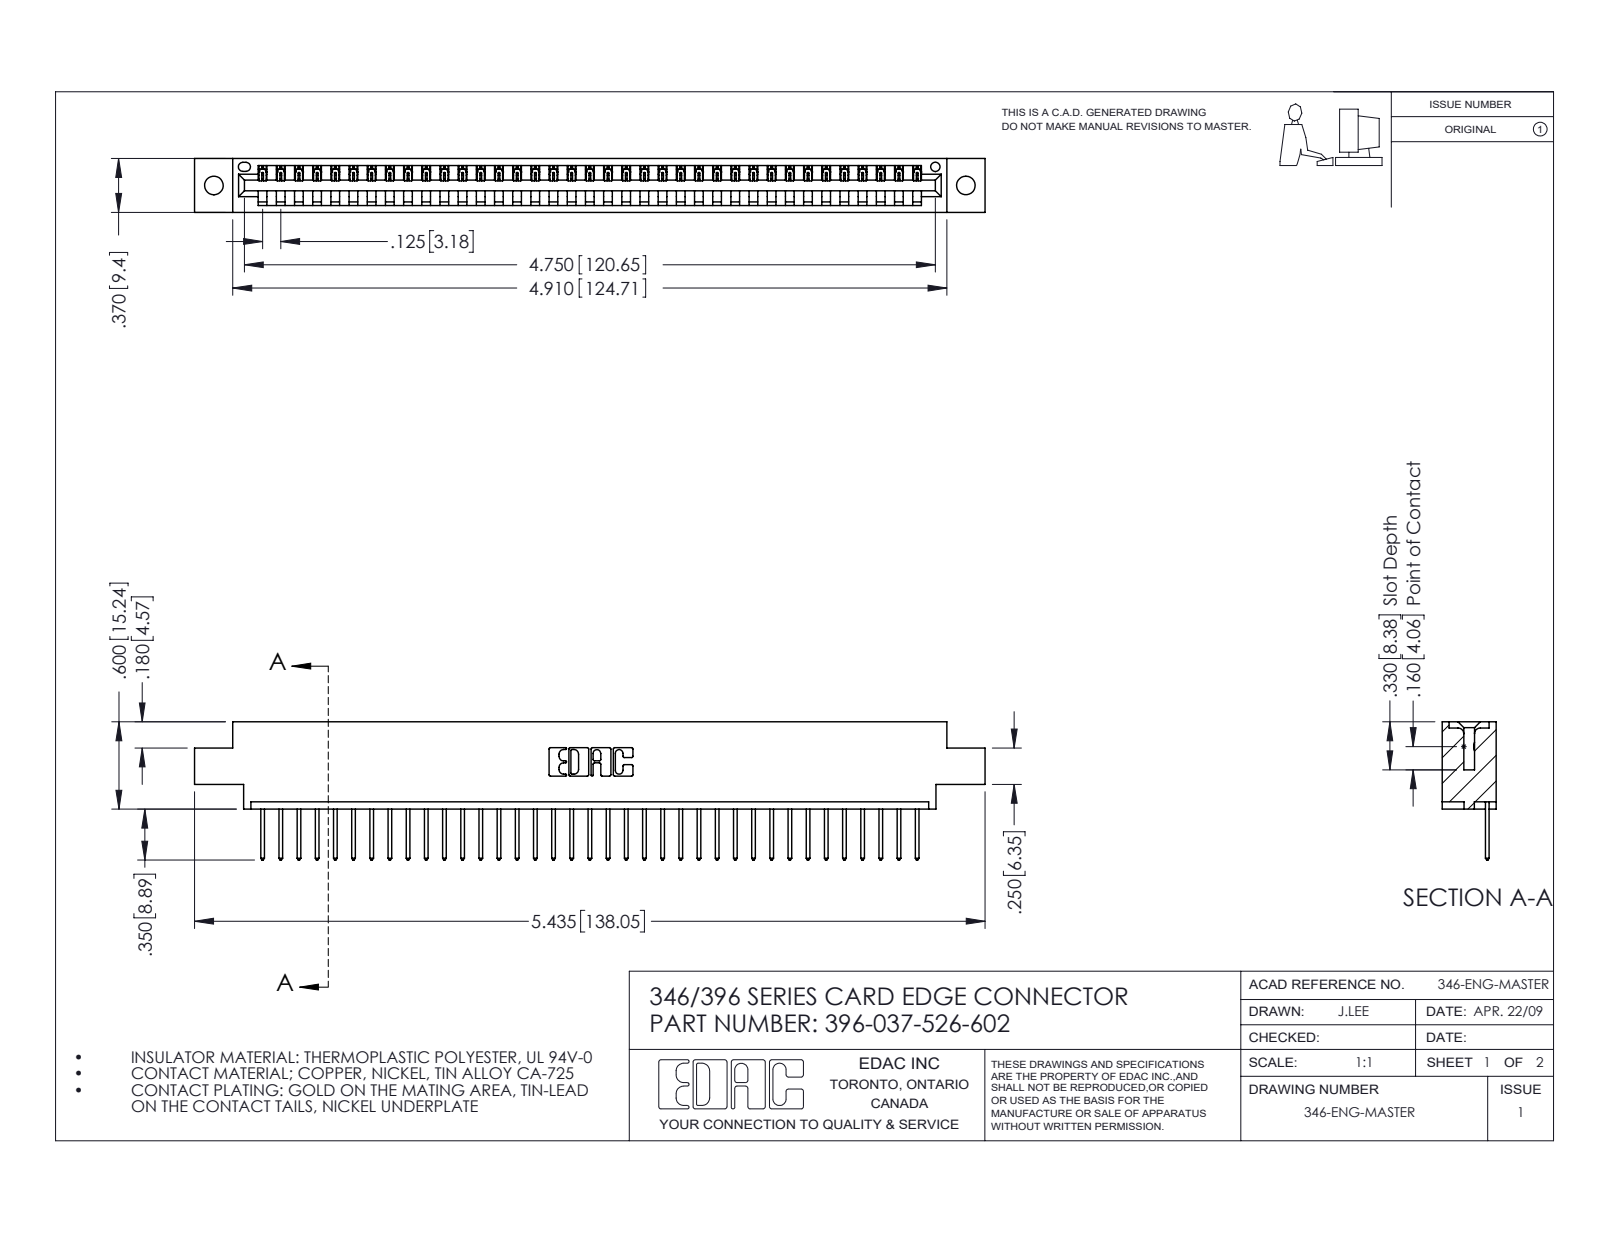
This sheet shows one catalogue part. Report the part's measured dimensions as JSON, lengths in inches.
{"part_name": "396-037-526-602; 345-292-001_345-293-126; 346 Part_0.170 Offset - 0.128 Dia", "step_written_by": "SolidWorks 2016 (CONFIG_CONTROL_DESIGN)", "units": "inches", "bodies": {"solids": 38, "faces": 2272, "planar": 1560, "cylindrical": 712, "other": 0}, "overall_size": [5.435, 0.95, 0.37], "volume_in3": 0.791, "surface_area_in2": 24.79, "round_holes": [[0.128, 2], [0.064, 1]], "partial_cylinders_radius": [[0.006, 74], [0.01, 74], [0.01, 22], [0.007, 6], [0.031, 6], [0.026, 3], [0.031, 2], [0.04, 2]], "face_to_face_distances": [0.048, 0.322, 0.37, 0.25, 0.072, 0.298, 0.025, 0.148, 0.222, 0.1], "hole_center_spacings": [0.246, 4.961, 5.17]}
